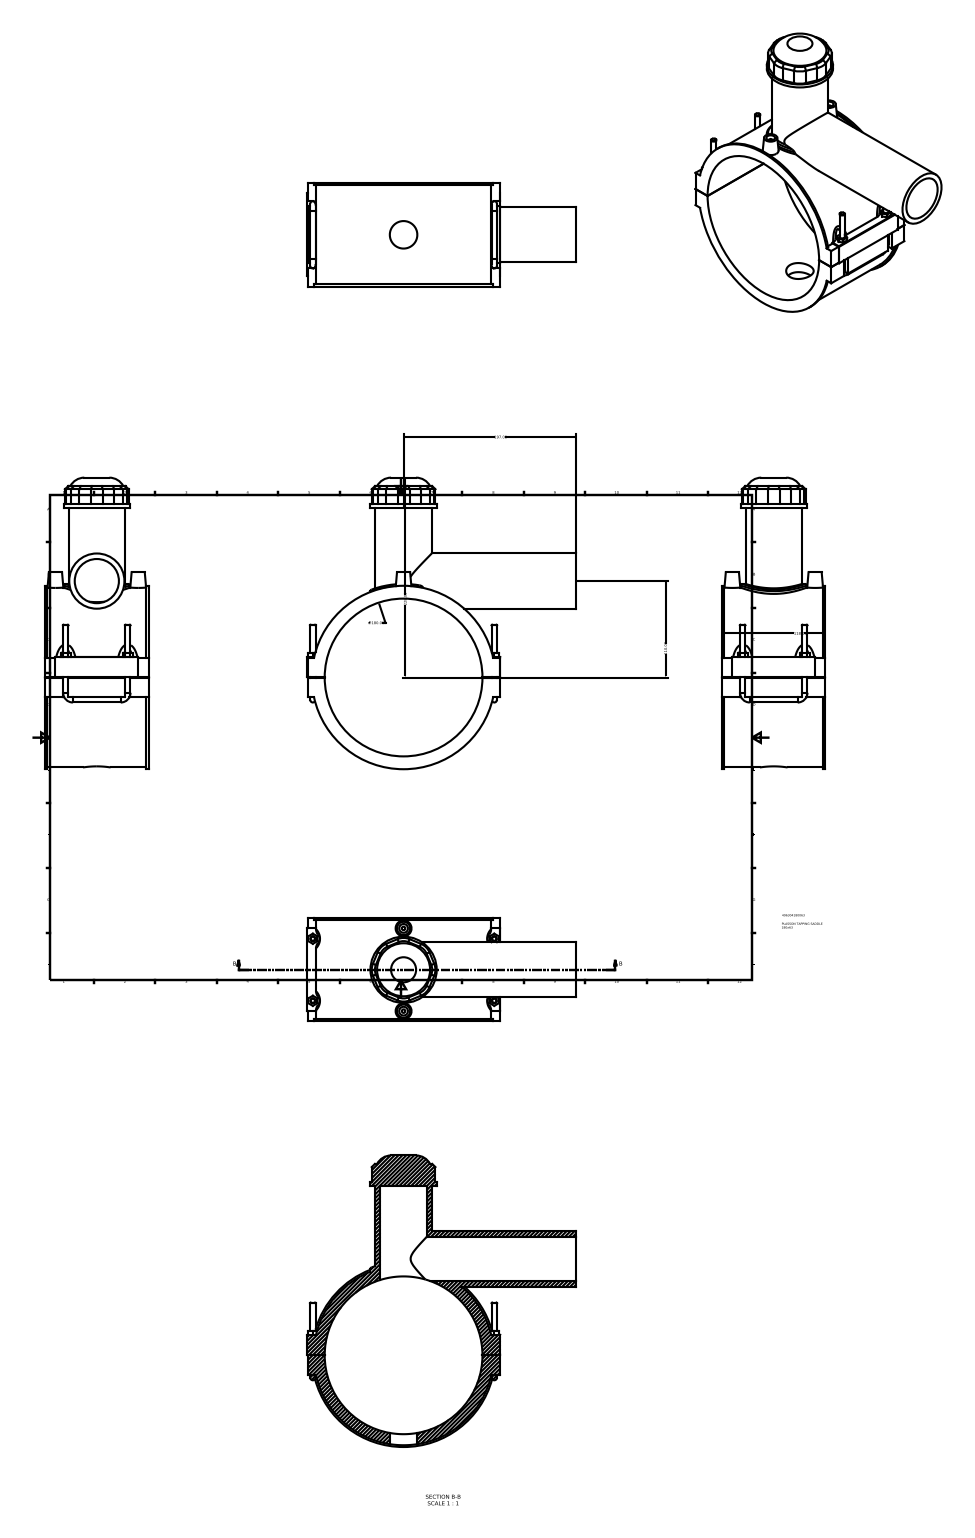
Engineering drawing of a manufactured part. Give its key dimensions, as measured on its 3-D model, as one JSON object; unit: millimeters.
{"part_name": "496304180063", "step_written_by": "Autodesk Inventor 2015 (AUTOMOTIVE_DESIGN)", "units": "millimeters", "bodies": {"solids": 1, "faces": 181, "planar": 110, "cylindrical": 47, "other": 24}, "overall_size": [332.65, 307.5, 118], "volume_mm3": 1352000, "surface_area_mm2": 287626, "round_holes": [[10, 2], [31.36, 1], [50.4, 1], [52.92, 1], [180, 1]], "round_bosses_or_shafts": [[6, 6], [4, 2], [209.3, 1], [205.2, 1], [75.6, 1], [64.26, 1], [63, 1]], "partial_cylinders_radius": [[18, 8], [3, 4], [7.5, 4], [0.5, 1], [106.7, 1]], "face_to_face_distances": [118, 1, 220, 193.55, 193.45, 219, 22.45, 22.55, 2.36, 115.64], "hole_center_spacings": [47.2, 94.4]}
